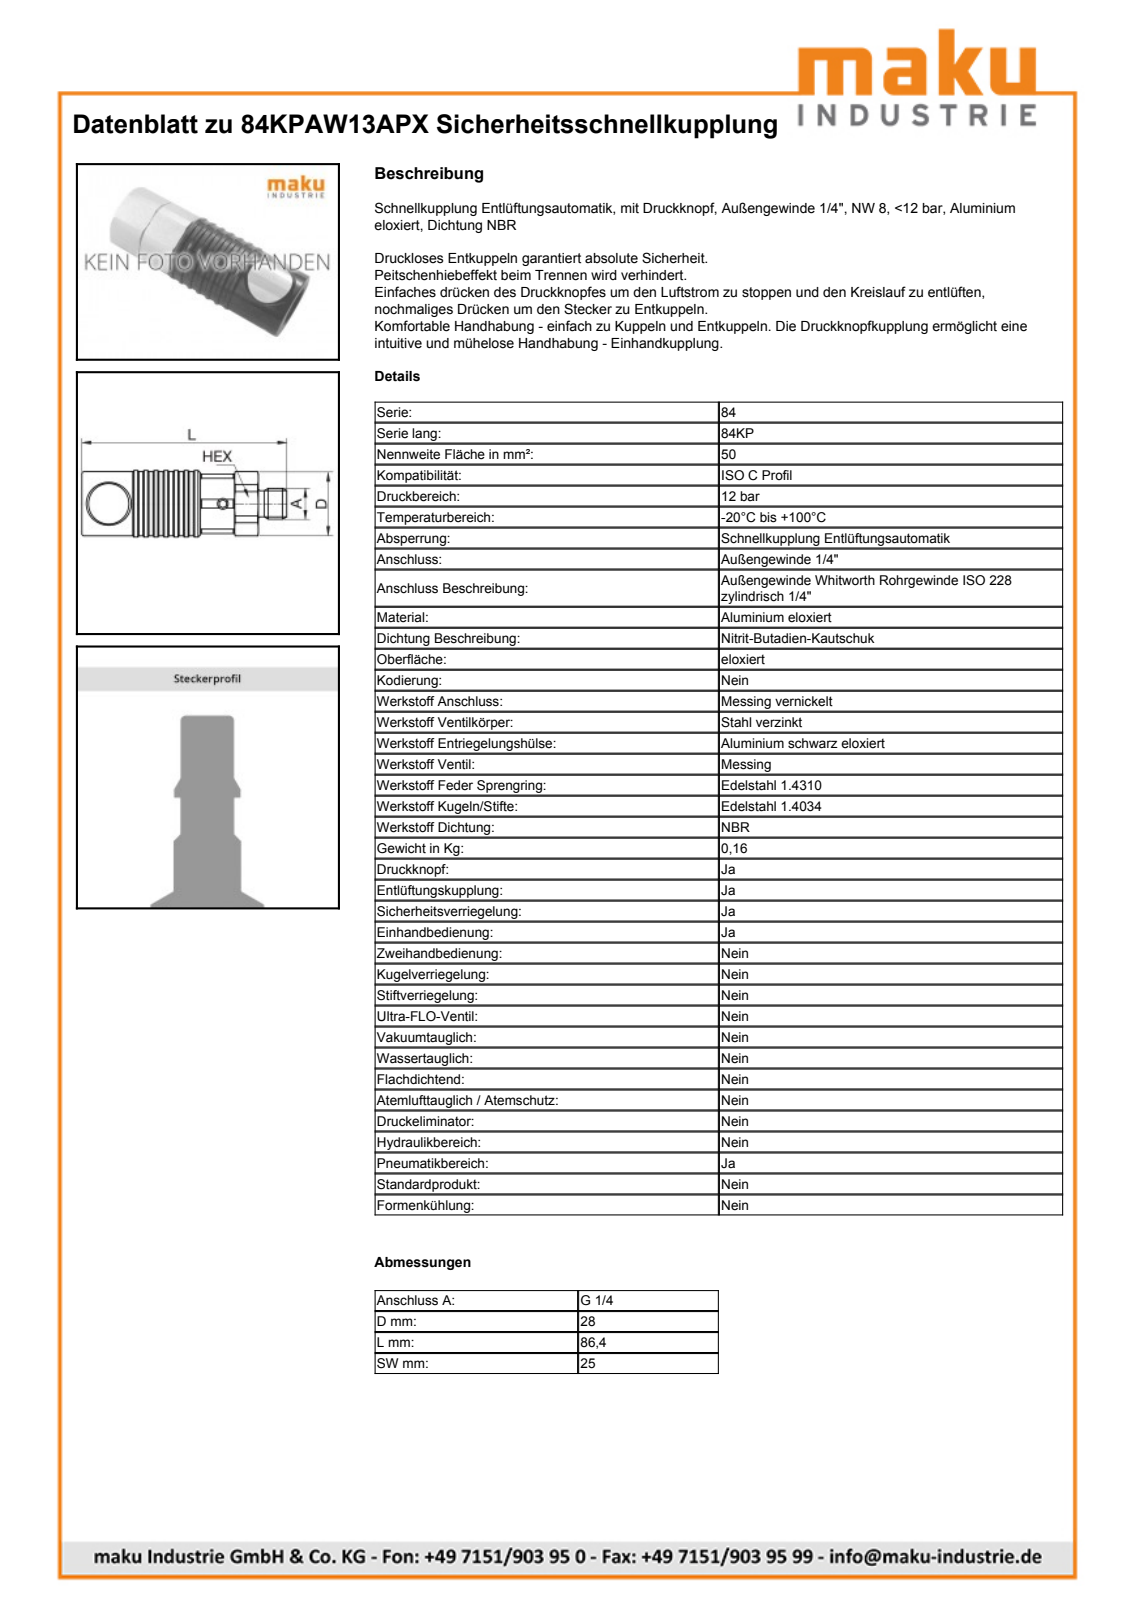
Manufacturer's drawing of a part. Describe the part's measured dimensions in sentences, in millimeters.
The part is named "84KPAW13APX". Its 3-D file was written by "Autodesk Inventor 2019 (CONFIG_CONTROL_DESIGN)". It is 33 solids with 340 faces: 115 planar, 117 cylindrical and 108 other. Overall it measures 85.4 by 28 by 28 millimeters. Its volume is 57 189 cubic millimeters and its surface area 32 560 square millimeters. Round holes: 2 of diameter 3.5, 2 of diameter 4, 2 of diameter 14.1, 1 of diameter 7.9, 1 of diameter 8, 1 of diameter 11.2, 1 of diameter 14, 1 of diameter 15.5, 1 of diameter 16.7, 1 of diameter 16.75, 1 of diameter 17.1, 1 of diameter 18. Round bosses or shafts: 1 of diameter 28, 1 of diameter 27, 1 of diameter 25, 1 of diameter 23.33, 1 of diameter 23.3, 1 of diameter 23, 1 of diameter 22.17, 1 of diameter 19.7. Partial cylindrical surfaces (rounded edges, fillets, slot ends): 1 of radius 5.53, 1 of radius 9.75, 1 of radius 13.5, 1 of radius 14.5. The main face-to-face distances are 25, 64.4, 35.3, 29.1, 24.3, 9, 22.7, 41.7, 6.4, 44.3. The hole center spacings are 1.3, 22, 26.1, 48.1.
